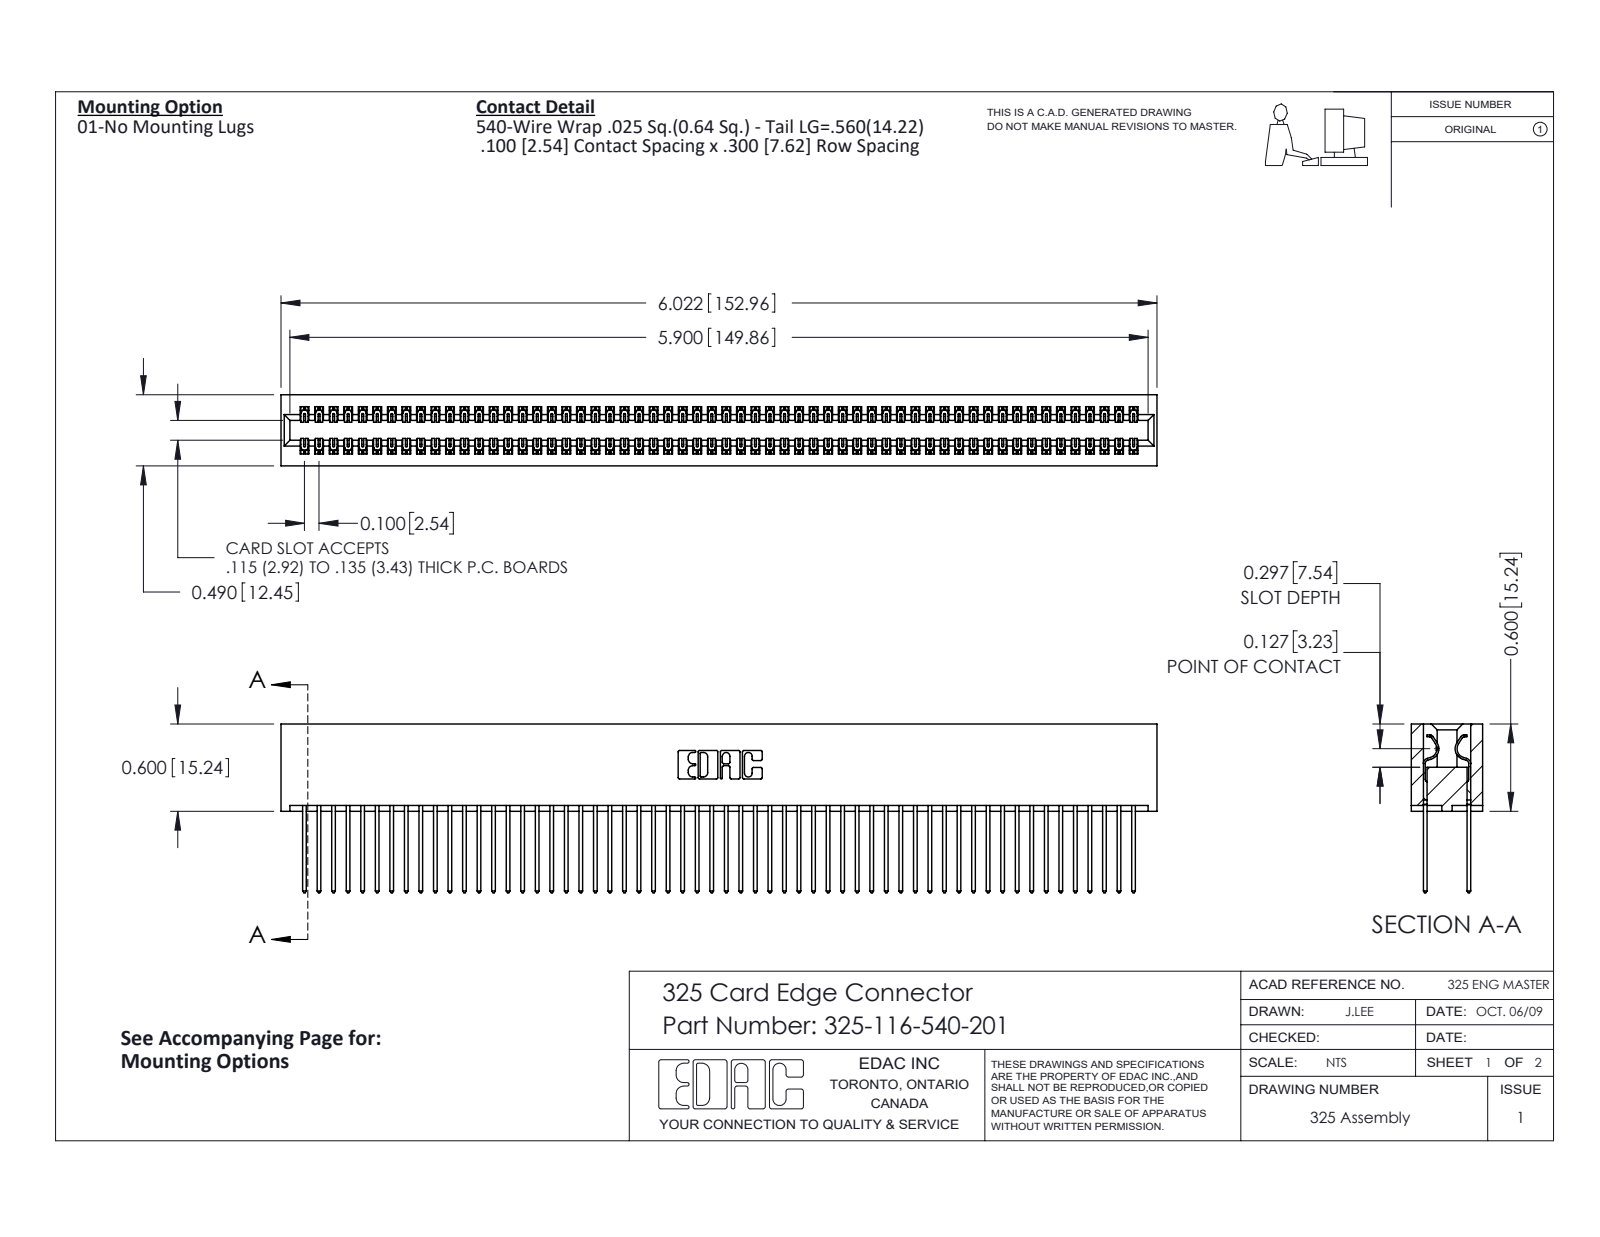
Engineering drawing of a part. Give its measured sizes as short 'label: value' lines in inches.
name: 325-116-540-201; 325-292-001_325-293-140; 325 Part_Lugless
written by: SolidWorks 2016 (CONFIG_CONTROL_DESIGN)
unit: in
bodies: 117 solids, 6138 faces (4242 planar, 1896 cylindrical, 0 other)
size: 6.022 × 1.16 × 0.49
volume: 1.278 in³; area: 44.13 in²
rounds: 174× R0.006, 116× R0.01, 22× R0.01, 6× R0.007, 6× R0.031, 3× R0.026, 2× R0.014, 2× R0.022
face distances: 0.083, 0.407, 0.3, 0.107, 0.383, 0.025, 0.325, 0.49, 0.275, 0.56
